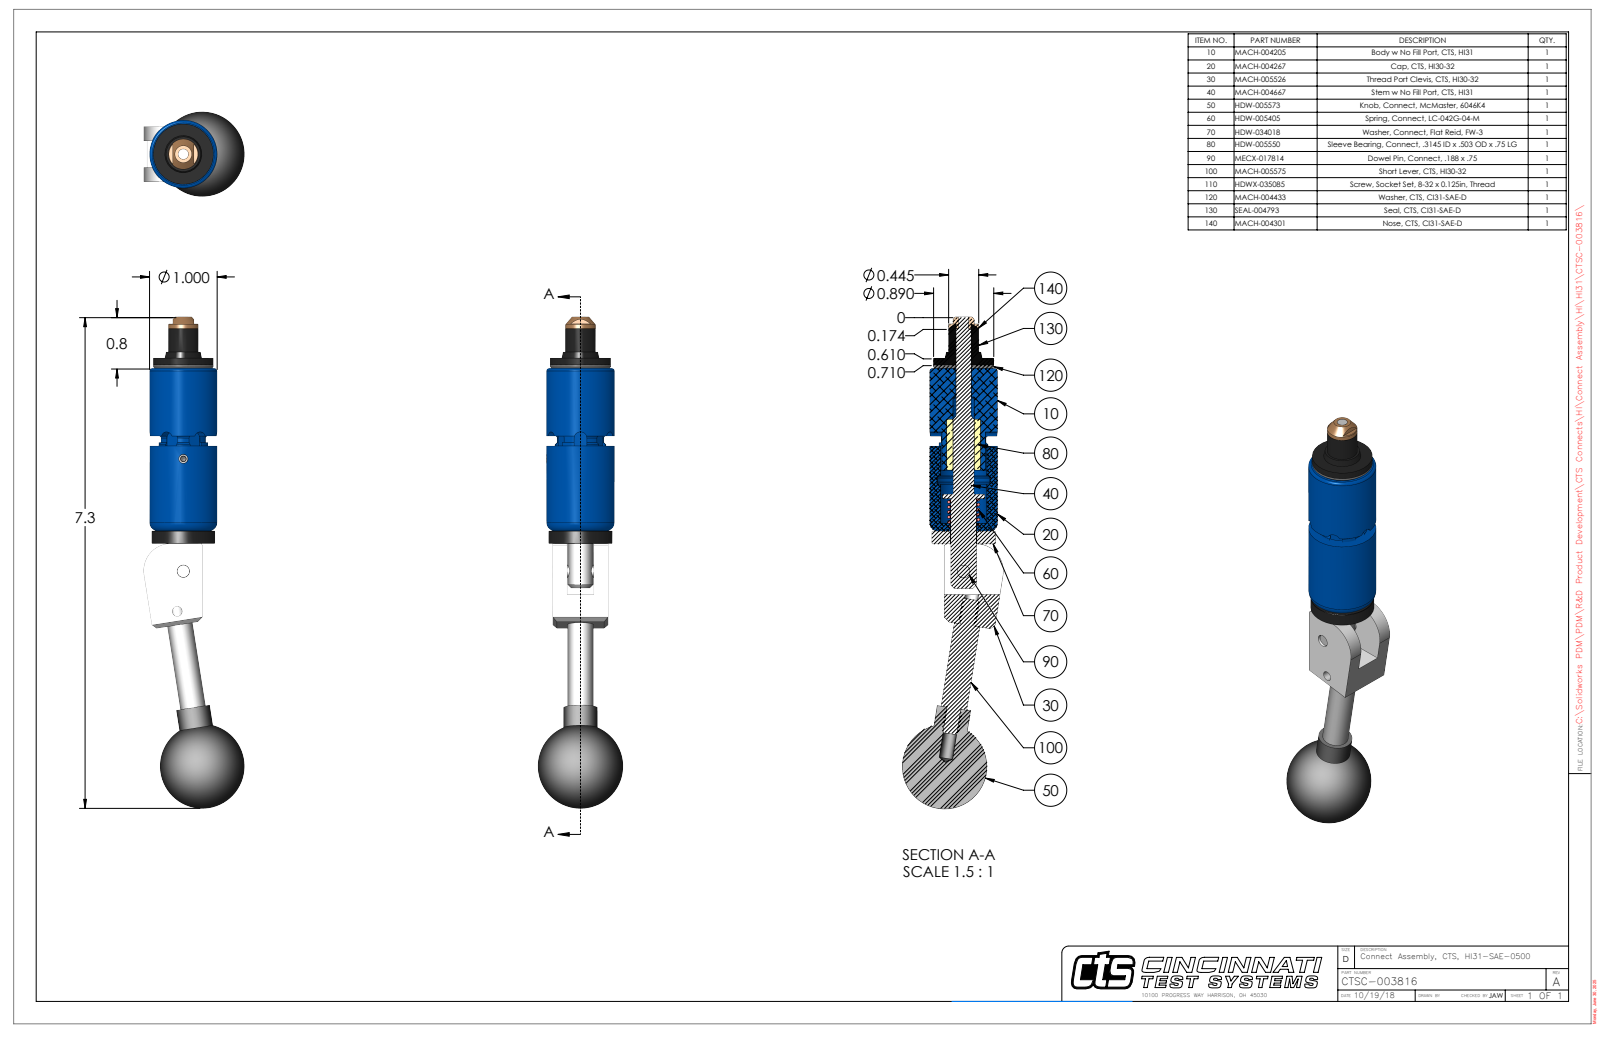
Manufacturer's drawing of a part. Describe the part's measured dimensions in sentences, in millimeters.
The part is named "CTSC-003816". Its 3-D file was written by "SolidWorks 2023 (AUTOMOTIVE_DESIGN)". It is 9 solids with 277 faces: 102 planar, 111 cylindrical and 64 other. Overall it measures 184.3 by 37.9 by 31.8 millimeters. Its volume is 64 370 cubic millimeters and its surface area 21 290 square millimeters. Round holes: 2 of diameter 3.8, 2 of diameter 5.1, 1 of diameter 3.5, 1 of diameter 4.8, 1 of diameter 5.8, 1 of diameter 5.8, 1 of diameter 9.8, 1 of diameter 10, 1 of diameter 17.5. Round bosses or shafts: 1 of diameter 25.4, 1 of diameter 23.8, 1 of diameter 22.6, 1 of diameter 12.7, 1 of diameter 11.3, 1 of diameter 11.3, 1 of diameter 9.7, 1 of diameter 9.5. Partial cylindrical surfaces (rounded edges, fillets, slot ends): 6 of radius 2.4, 2 of radius 0.7, 1 of radius 9.5, 1 of radius 10.2, 1 of radius 11.8. The main face-to-face distances are 5.3, 15.3, 1.3, 62.2, 60.9, 20.6, 67, 65.7, 4.7, 9.9. The hole center spacings are 15.2, 42.1, 57.2.
